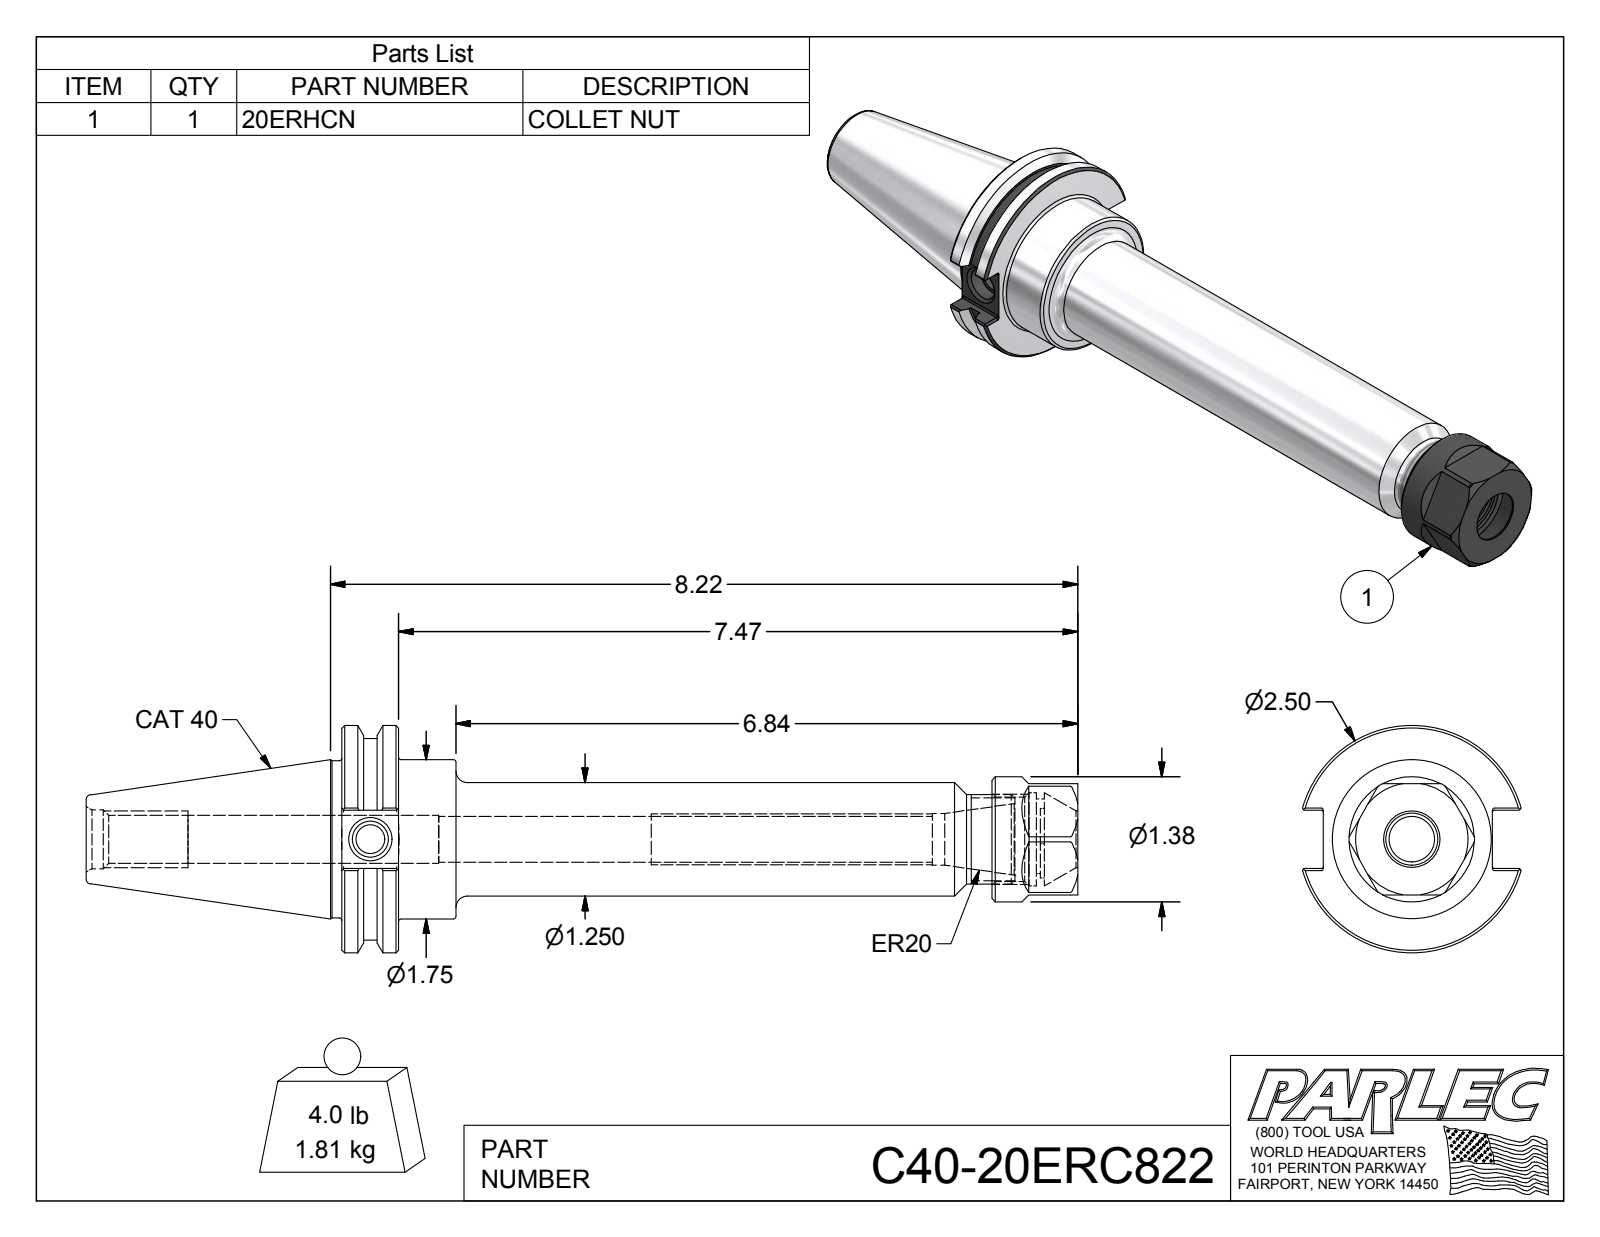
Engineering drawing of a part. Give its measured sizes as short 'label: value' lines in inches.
name: C40-20ER8-1; 20ERHCN; C40-20ERC822
written by: Autodesk Inventor 2016 (AUTOMOTIVE_DESIGN)
unit: in
bodies: 2 solids, 126 faces (50 planar, 35 cylindrical, 41 other)
size: 10.907 × 2.5 × 2.404
volume: 14.13 in³; area: 77.78 in²
holes: 1× ⌀0.315, 1× ⌀0.399, 1× ⌀0.502, 1× ⌀0.526, 1× ⌀0.527, 1× ⌀0.57, 1× ⌀0.62, 1× ⌀0.648, 1× ⌀0.82, 1× ⌀0.925, 1× ⌀1.024
bosses: 1× ⌀2.5, 1× ⌀2.219, 1× ⌀1.75, 1× ⌀1.73, 1× ⌀1.378, 1× ⌀1.25, 1× ⌀0.984
rounds: 12× R0.02, 1× R0.423
face distances: 0.625, 1.22, 8.095, 7.47, 7.15, 6.525, 0.945, 1.255, 0.63, 5.895
hole spacings: 0.037
